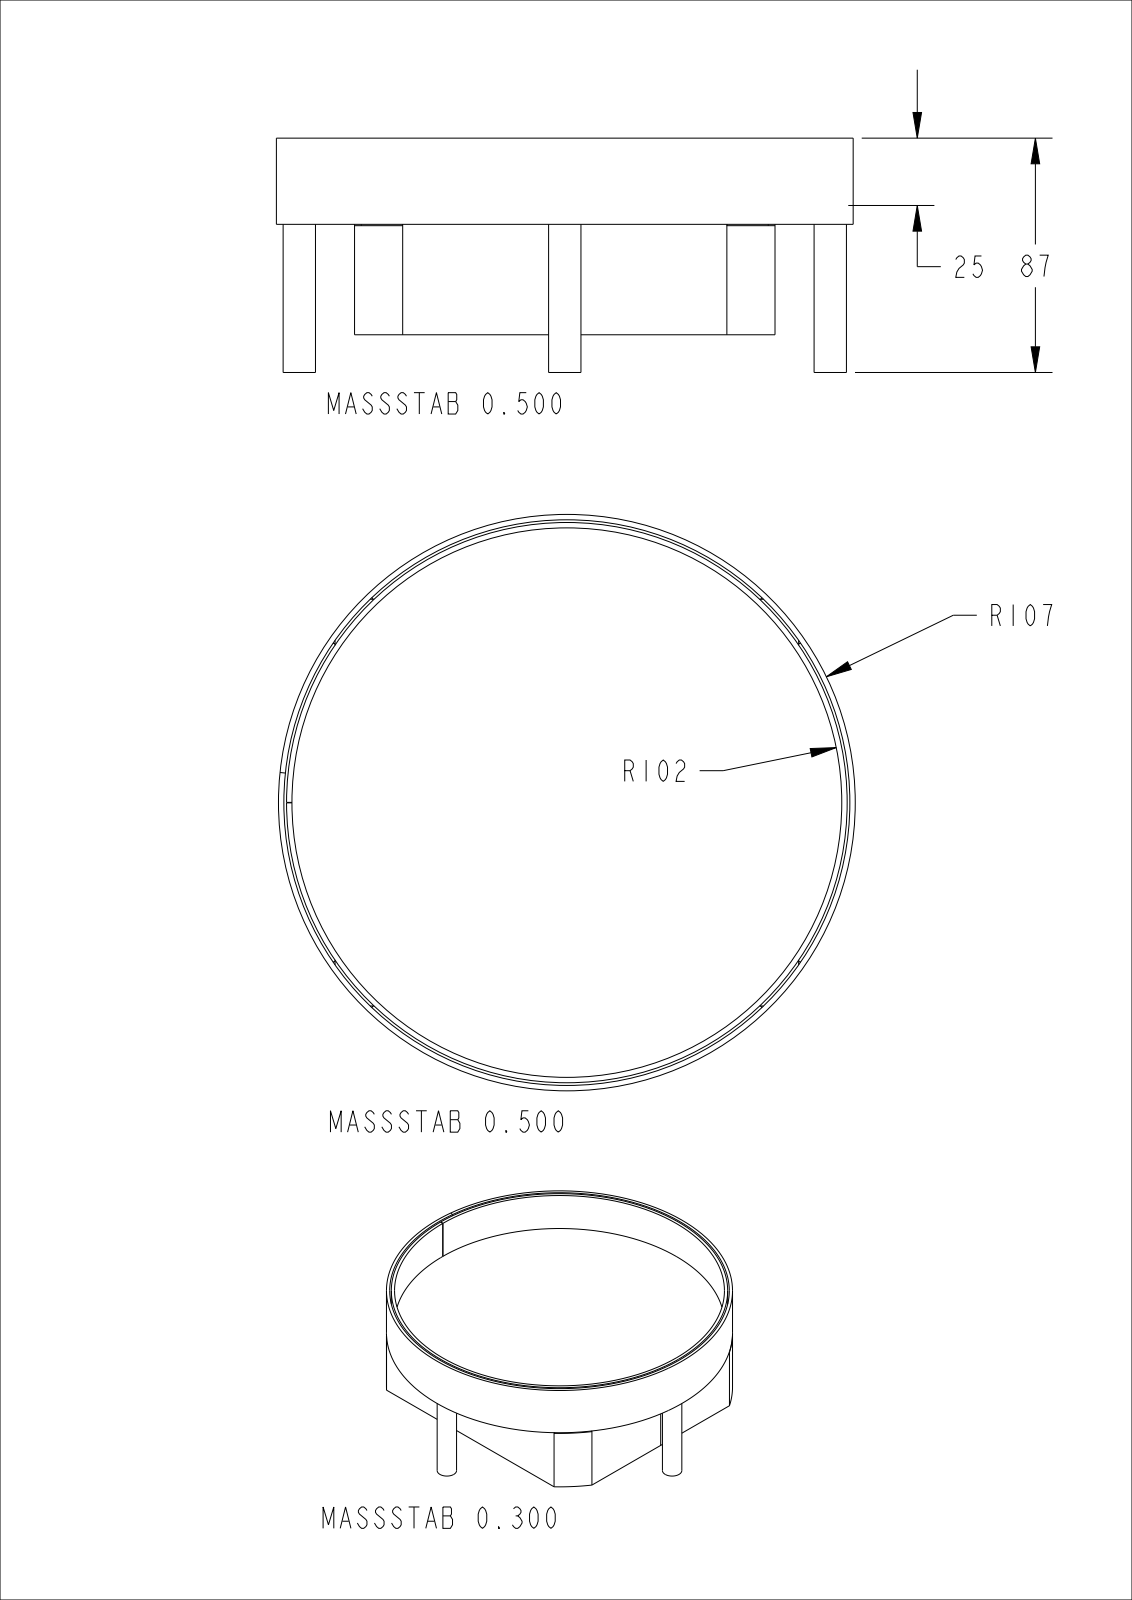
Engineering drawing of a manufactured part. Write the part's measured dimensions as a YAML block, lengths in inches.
part_name: "T-00671; T-00672; T-00673; T-00675 (+8 more)"
step_written_by: "CREO PARAMETRIC BY PTC INC, 2022024 (AUTOMOTIVE_DESIGN)"
units: inches
bodies: {solids: 8, faces: 155, planar: 95, cylindrical: 60, other: 0}
overall_size: [8.425, 8.425, 3.425]
volume: 13.54
surface_area: 403.1
round_holes:
  - {diameter: 0.15, count: 6}
  - {diameter: 0.398, count: 4}
  - {diameter: 8.268, count: 1}
round_bosses_or_shafts:
  - {diameter: 0.472, count: 4}
  - {diameter: 0.388, count: 4}
  - {diameter: 8.425, count: 1}
  - {diameter: 8.189, count: 1}
  - {diameter: 8.031, count: 1}
partial_cylinders:
  - {radius: 0.02, count: 8}
face_to_face_distances: [0.079, 0.098, 0.197, 6.87, 6.043, 0.276, 0.118, 6.772, 6.969, 5.945]
hole_center_spacings: [1.62, 3.834, 3.878, 4.187, 5.484, 6.477, 7.54, 0.867]
